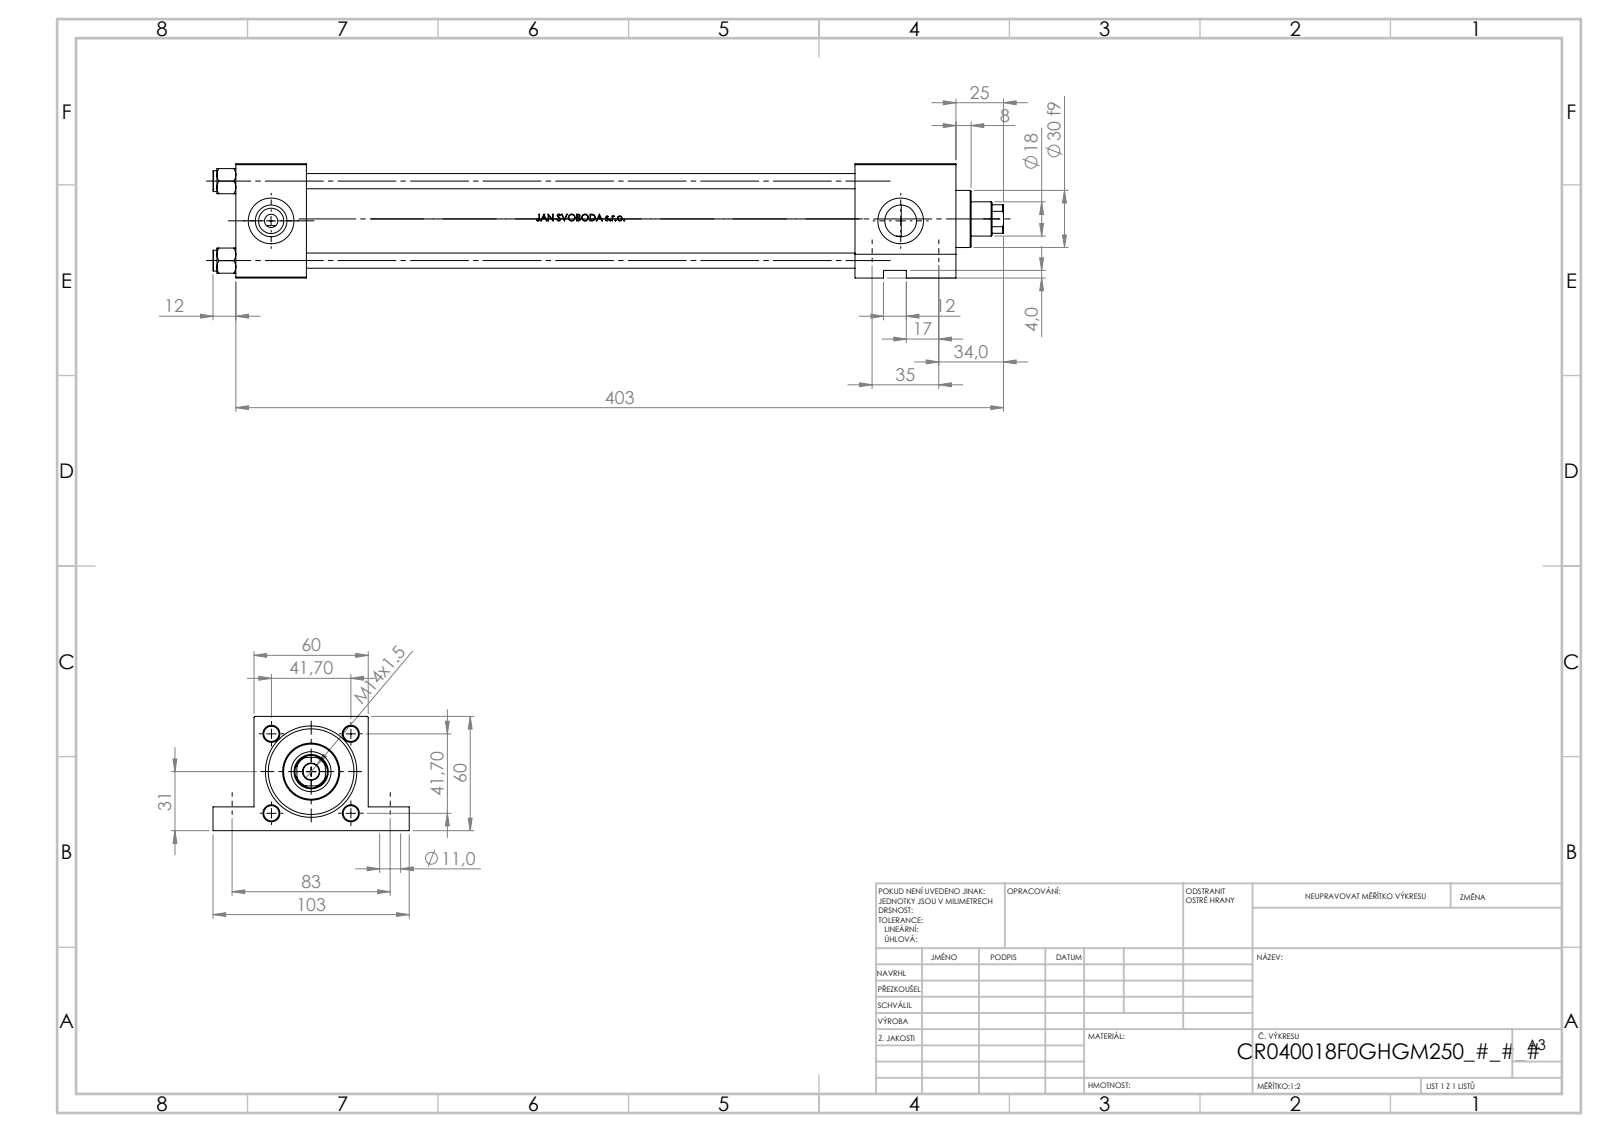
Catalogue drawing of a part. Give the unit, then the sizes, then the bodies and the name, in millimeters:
Units: millimetres
Overall size (bounding box): 415 × 103 × 60
Round holes (diameter × count): ⌀8 ×4, ⌀11 ×4, ⌀7 ×2, ⌀16.66 ×2, ⌀24 ×2, ⌀8.5 ×1, ⌀18 ×1, ⌀21 ×1, ⌀31 ×1, ⌀40 ×1, ⌀45 ×1
Round bosses / shafts (diameter × count): ⌀11 ×4, ⌀46 ×1, ⌀30 ×1
Partial cylindrical surfaces — rounded edges, fillets, slot ends (radius × count): R8.5 ×1
Main face-to-face distances: 60, 37, 378, 341, 325, 288, 53, 349.3, 312.3, 24.3
Hole centre spacings: 41.7, 28.79, 30.2, 35, 58.97, 83, 90.08, 330.5
Volume: 621 614 mm³ · Surface area: 209 806 mm²
Bodies: 11 solids, 1118 faces (437 planar, 141 cylindrical, 540 other)
Part name (STEP PRODUCT): V215CR_F_Body; V215CR_F_TYCINKA; NUT_M5_F; V215CR_VCP_F (+1 more)
STEP written by: SolidWorks 2019 (CONFIG_CONTROL_DESIGN)
